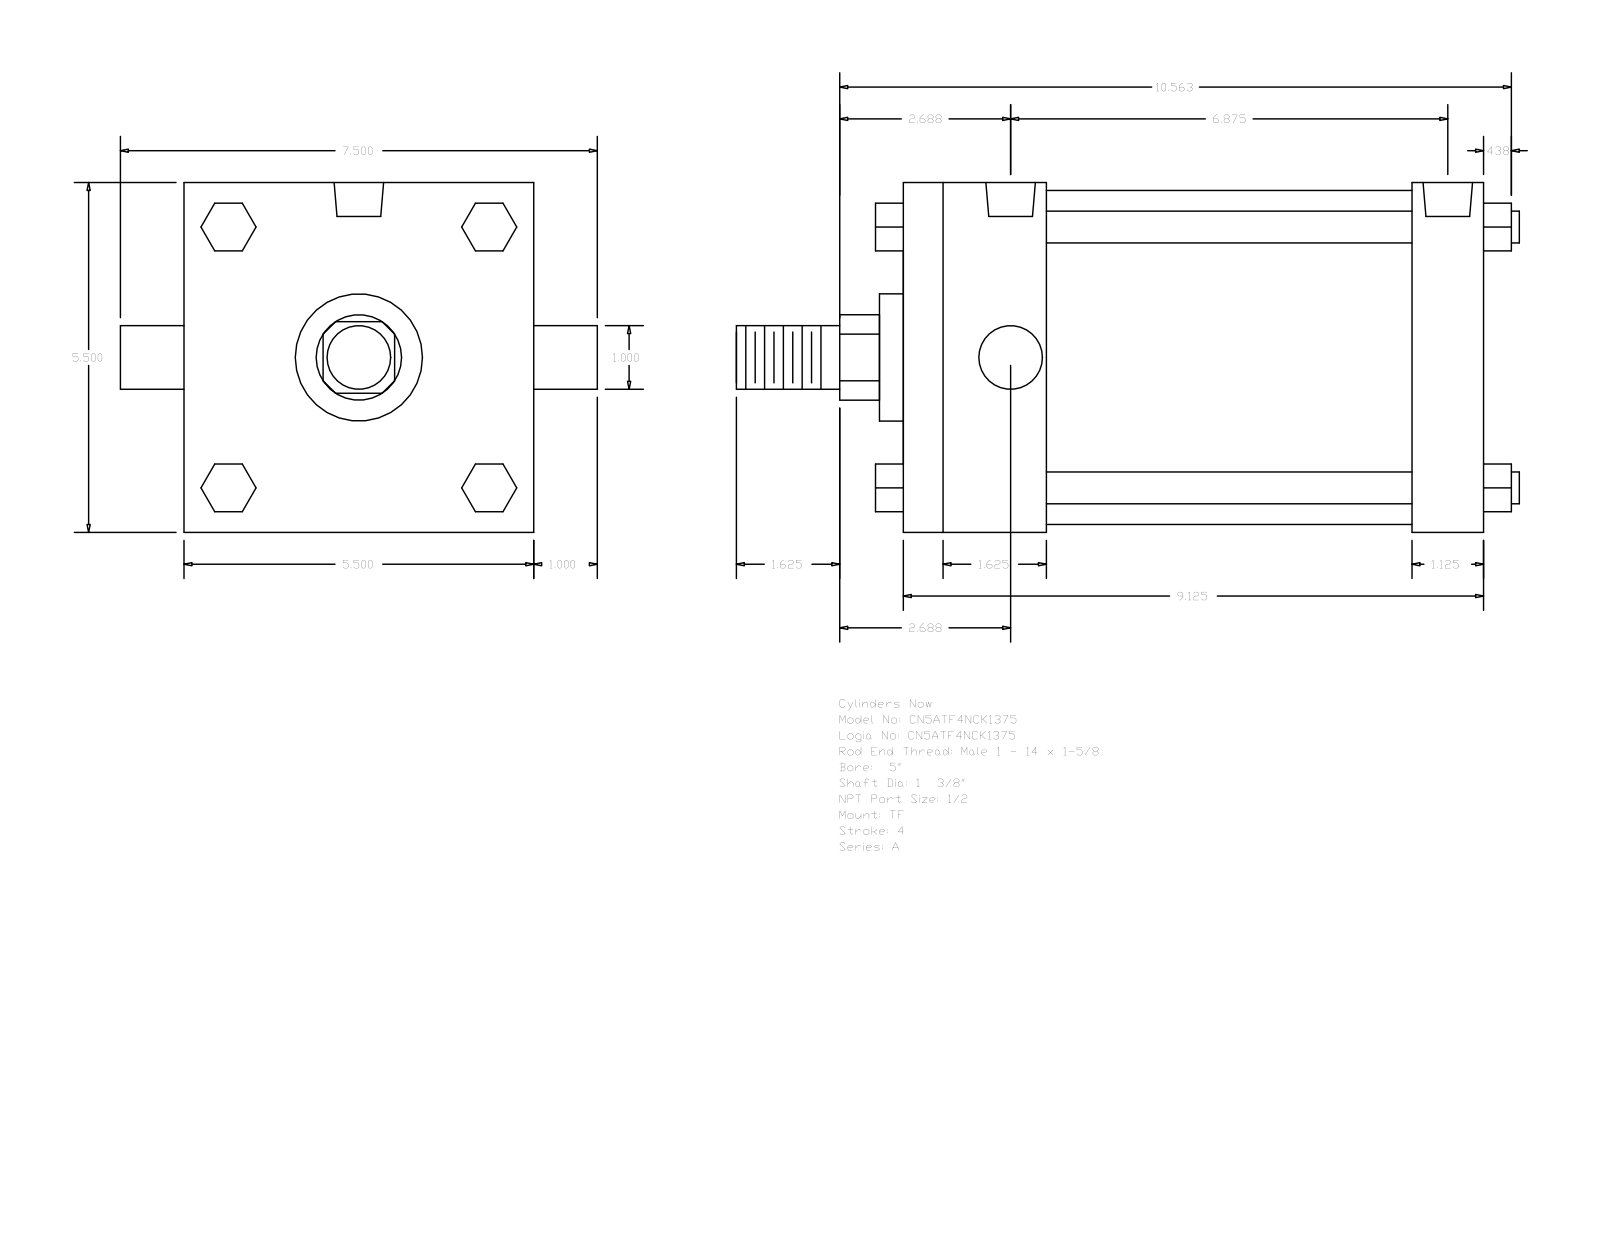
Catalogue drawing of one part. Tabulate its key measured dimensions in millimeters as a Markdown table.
| quantity | value |
| --- | --- |
| part name | A_TF__0500_1.375 |
| STEP written by | GSSL Pune (CONFIG_CONTROL_DESIGN) |
| units | millimeters |
| bodies | 0 solids, 120 faces (92 planar, 28 cylindrical, 0 other) |
| overall size | 312.74 × 190.5 × 139.7 |
| round holes (diameter × count) | 8.73 × 3, 19.77 × 2 |
| round bosses / shafts (diameter × count) | 12.7 × 4, 25.4 × 2, 133.35 × 1, 50.8 × 1, 34.92 × 1 |
| partial cylindrical surfaces (radius × count) | 17.06 × 1 |
| main face-to-face distances | 139.7, 231.78, 57.15, 28.58, 203.2, 146.05, 174.63, 19.05, 52.07, 90.18 |
| hole center spacings | 2.39, 172.24, 169.85, 174.63 |
